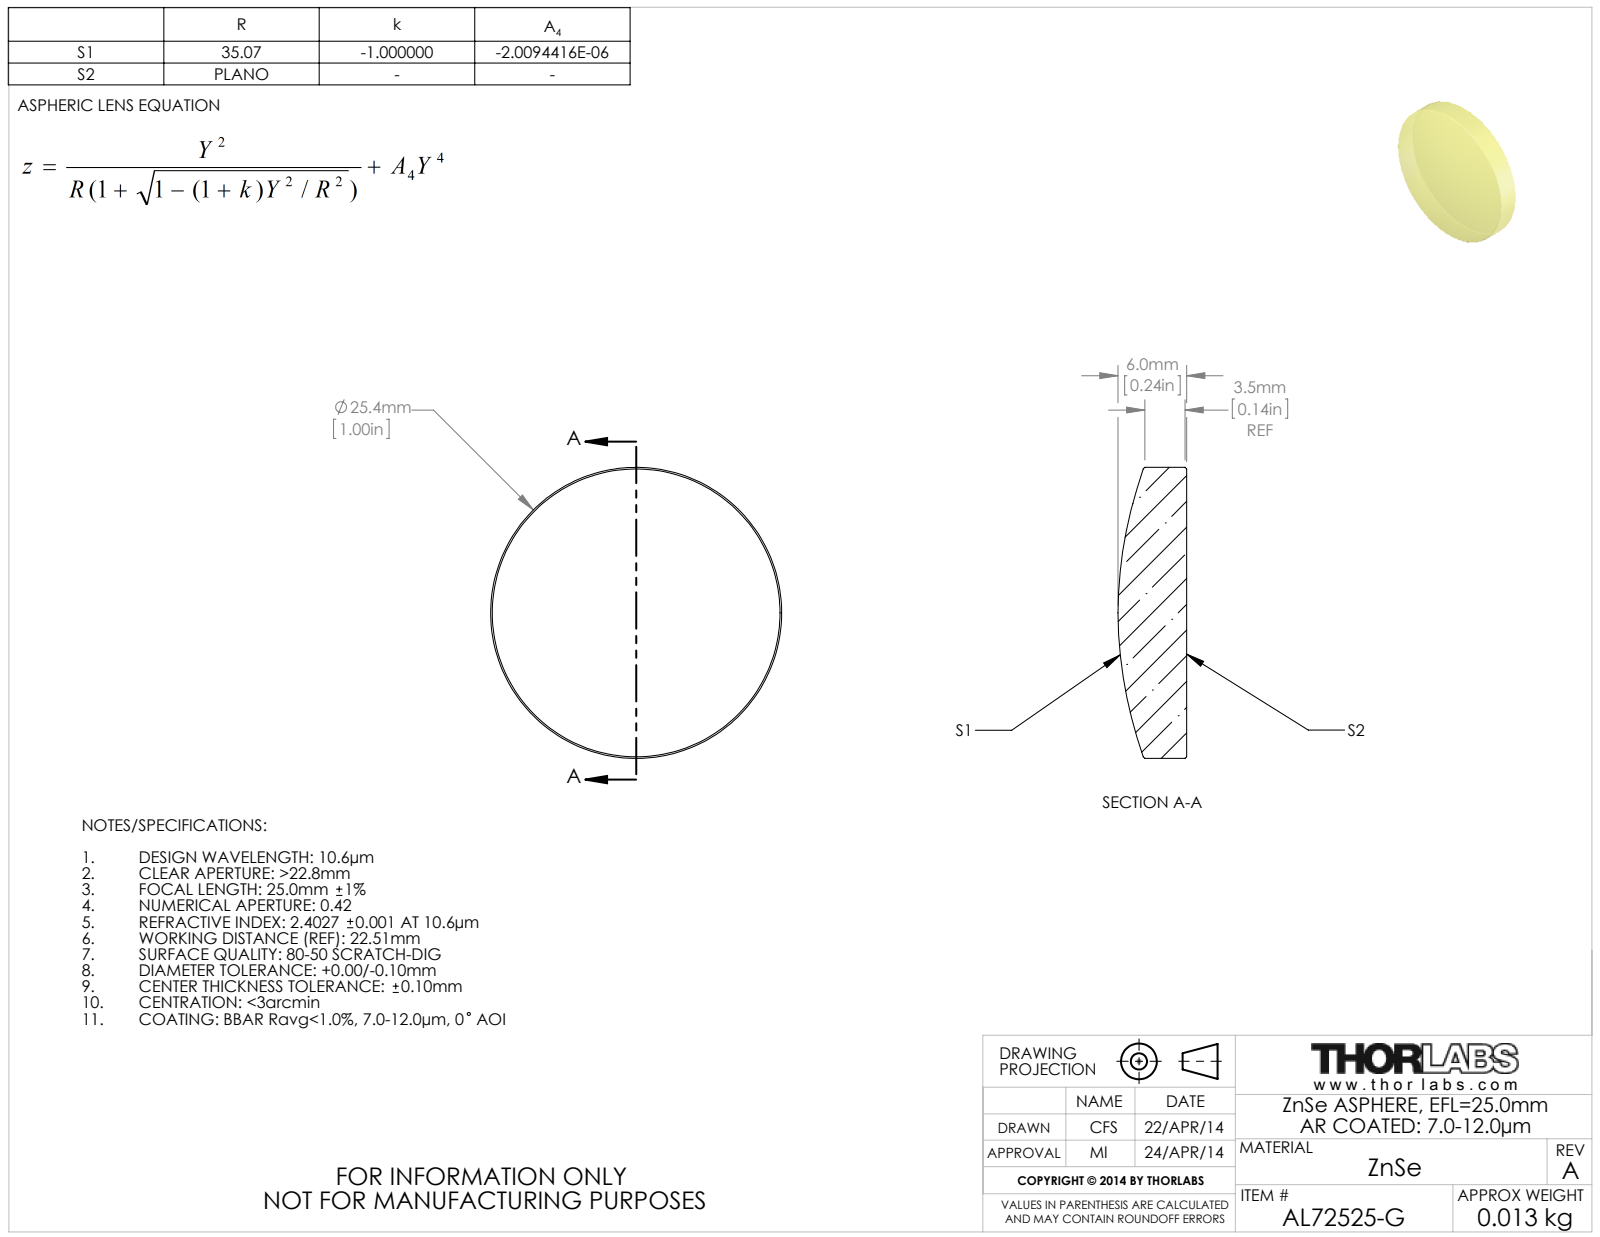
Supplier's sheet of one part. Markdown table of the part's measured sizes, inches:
| quantity | value |
| --- | --- |
| part name | TTN026908-E0W |
| STEP written by | SolidWorks 2012 (CONFIG_CONTROL_DESIGN) |
| units | inches |
| bodies | 1 solid, 9 faces (1 planar, 2 cylindrical, 6 other) |
| overall size | 1 × 1 × 0.236 |
| volume | 0.15 in³ |
| surface area | 2.043 in² |
| round bosses / shafts (diameter × count) | 1 × 1 |
